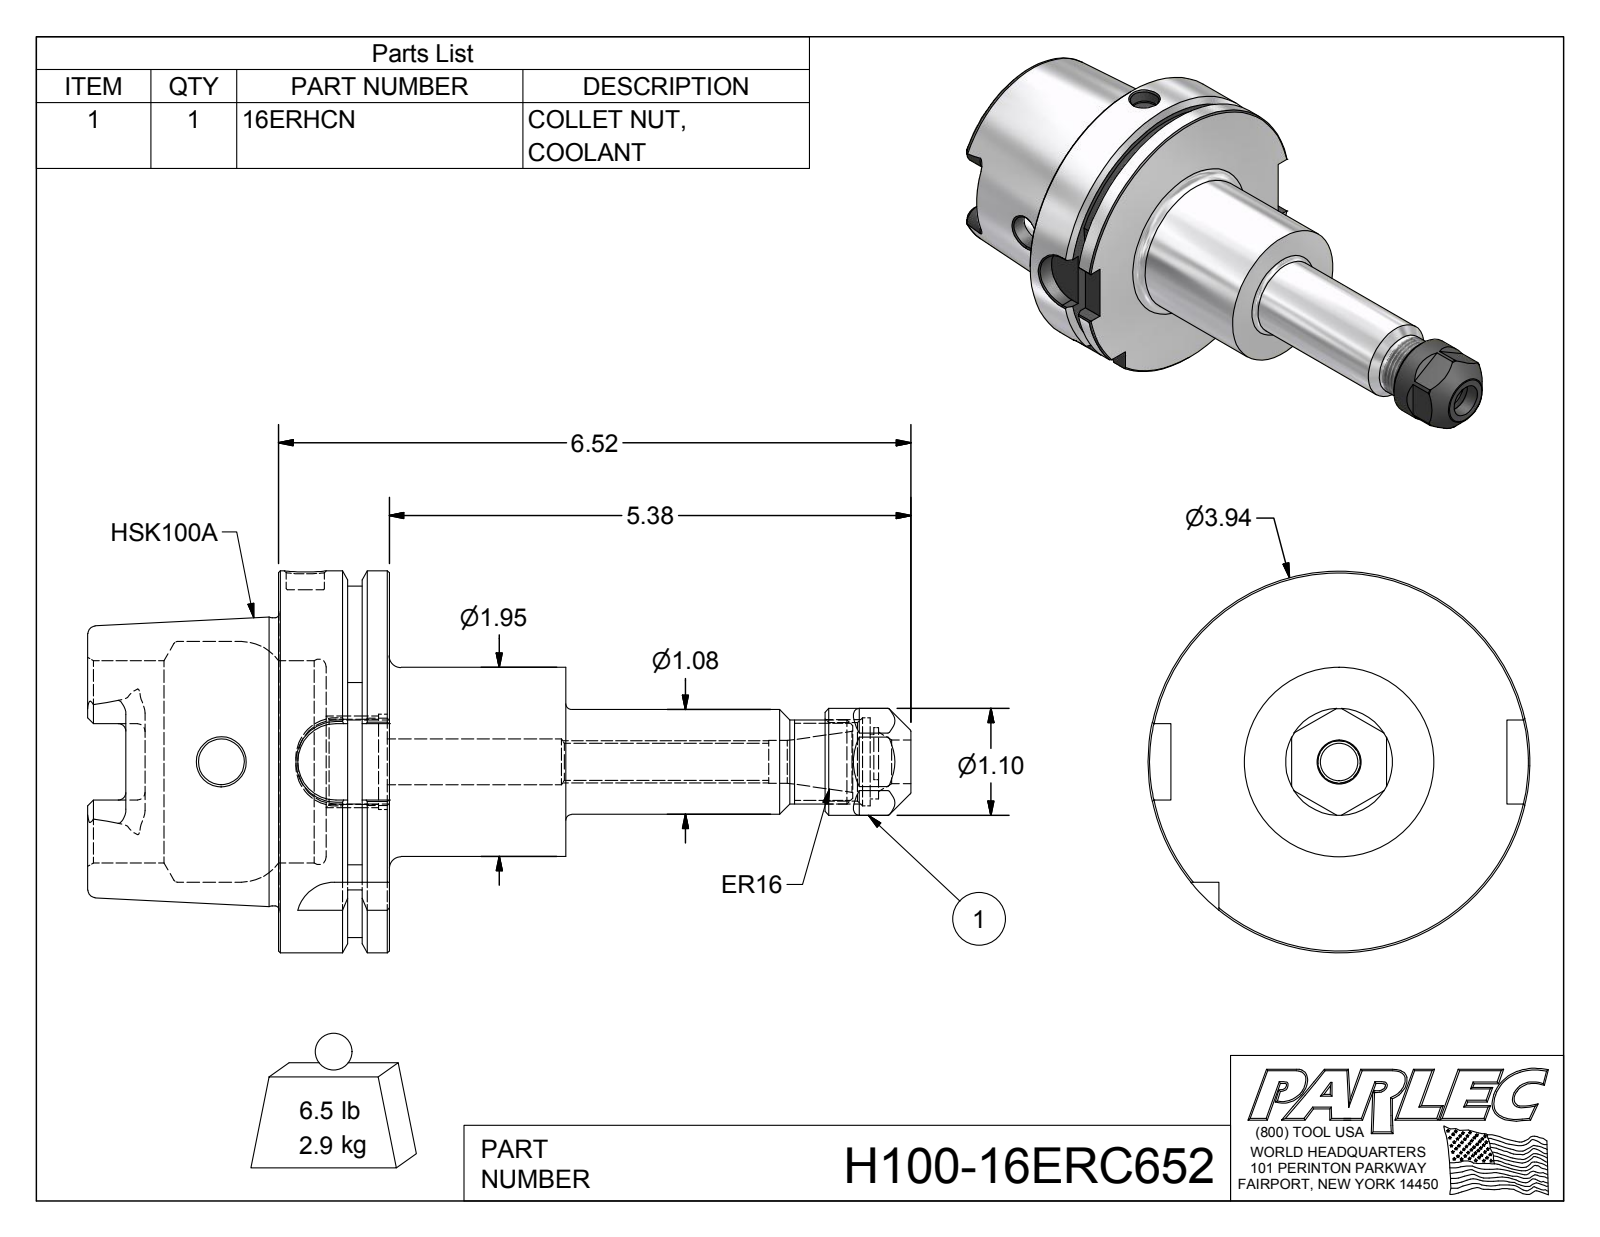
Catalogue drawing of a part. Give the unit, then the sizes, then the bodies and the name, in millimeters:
Units: millimetres
Overall size (bounding box): 215.6 × 100 × 100
Round holes (diameter × count): ⌀12 ×2, ⌀9.7 ×1, ⌀10 ×1, ⌀11.2 ×1, ⌀11.5 ×1, ⌀12 ×1, ⌀16.8 ×1, ⌀20.5 ×1, ⌀22.4 ×1, ⌀23 ×1, ⌀25 ×1, ⌀53 ×1
Round bosses / shafts (diameter × count): ⌀100 ×1, ⌀75.4 ×1, ⌀49.5 ×1, ⌀28 ×1, ⌀27.4 ×1, ⌀22 ×1
Partial cylindrical surfaces — rounded edges, fillets, slot ends (radius × count): R2 ×6, R4.9 ×4, R10 ×4, R9 ×1, R46 ×1
Main face-to-face distances: 29, 12.5, 16.5, 75.2, 62.7, 46.2, 50, 62.5, 79, 125.2
Hole centre spacings: 1.3
Volume: 377 700 mm³ · Surface area: 70 900 mm²
Bodies: 2 solids, 168 faces (62 planar, 43 cylindrical, 63 other)
Part name (STEP PRODUCT): H100-16ERC652; H100-16ER6-1; 16ERHCN
STEP written by: Autodesk Inventor 2012 (AUTOMOTIVE_DESIGN)
